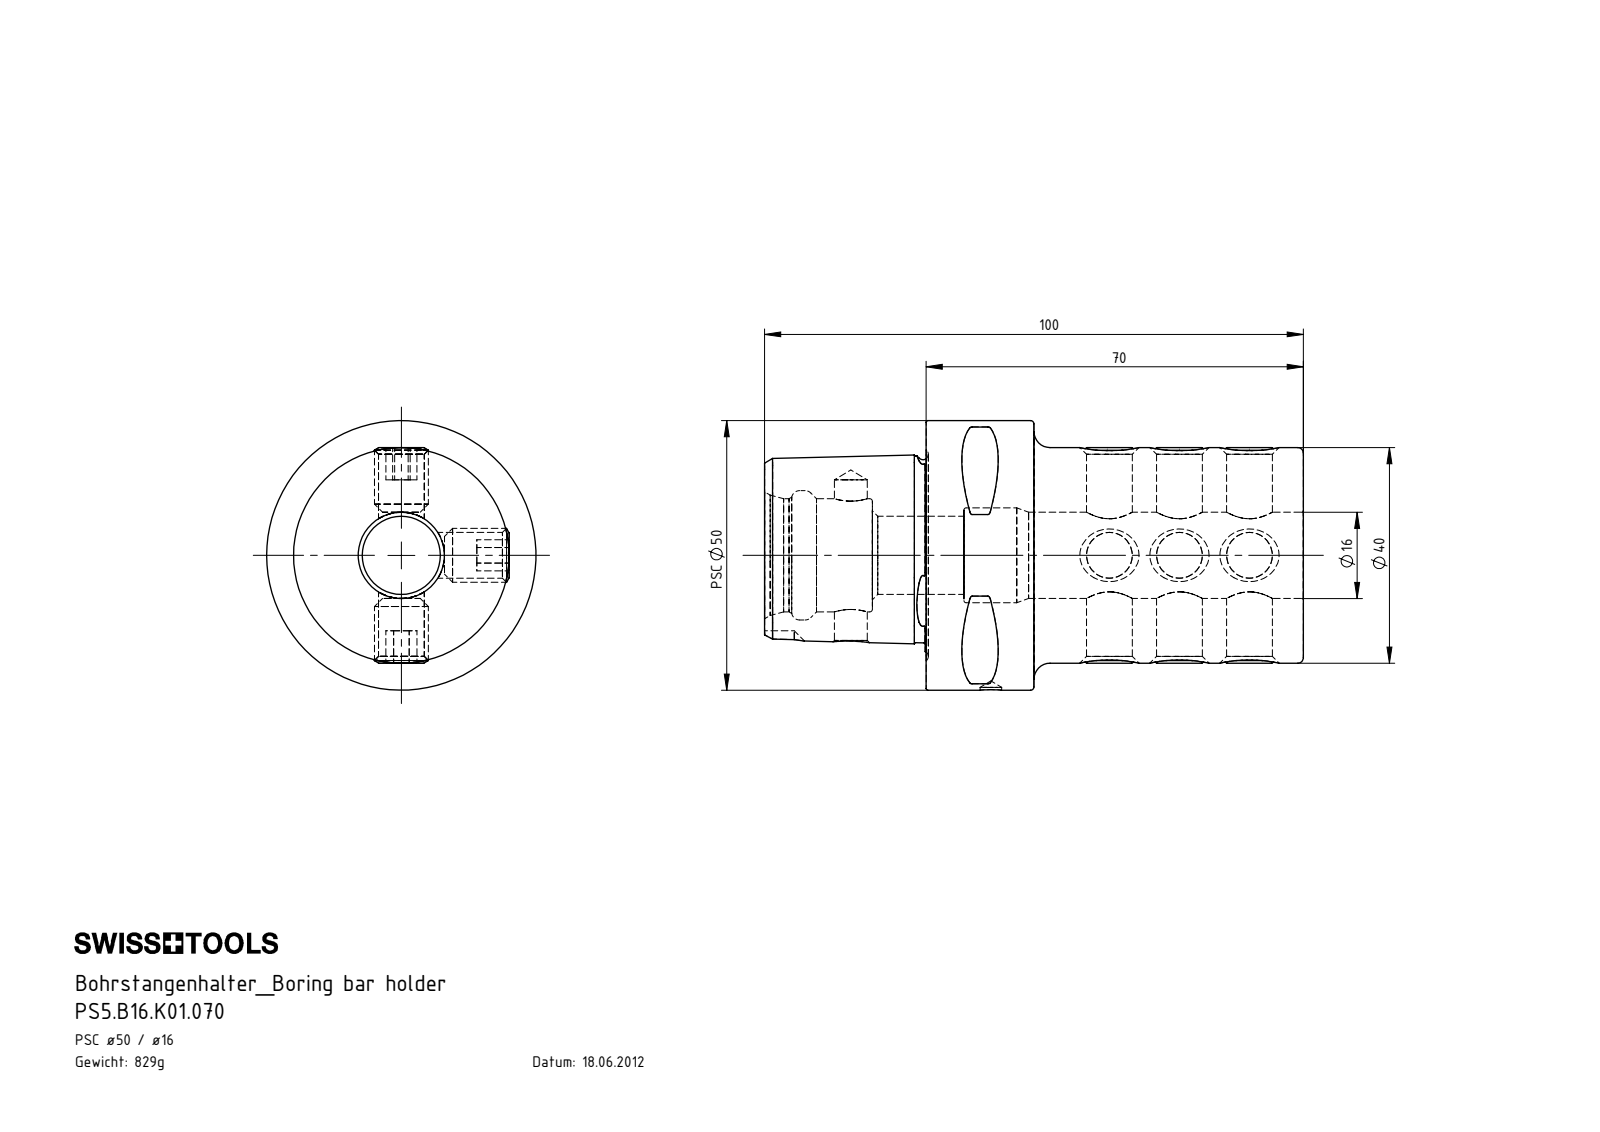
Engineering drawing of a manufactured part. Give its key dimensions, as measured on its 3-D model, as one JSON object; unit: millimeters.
{"part_name": "PS5-B16.K01.070_A; PS5.B16.K01.070; ISO 4026 - M10 x 12_PreviewCfg", "step_written_by": "SolidWorks 2017 (AUTOMOTIVE_DESIGN)", "units": "millimeters", "bodies": {"solids": 10, "faces": 322, "planar": 102, "cylindrical": 67, "other": 153}, "overall_size": [100, 50, 50], "volume_mm3": 105523, "surface_area_mm2": 28665, "round_holes": [[8.5, 6], [4, 1], [6.1, 1], [14.5, 1], [16, 1], [17.6, 1], [21, 1], [24, 1]], "round_bosses_or_shafts": [[10, 6], [50, 1], [40, 1]], "partial_cylinders_radius": [[0.5, 8], [4, 1]], "face_to_face_distances": [70, 30, 50, 5, 100, 6, 20, 6.5, 19.18, 28], "hole_center_spacings": [13, 26, 48, 22, 35, 61, 74]}
